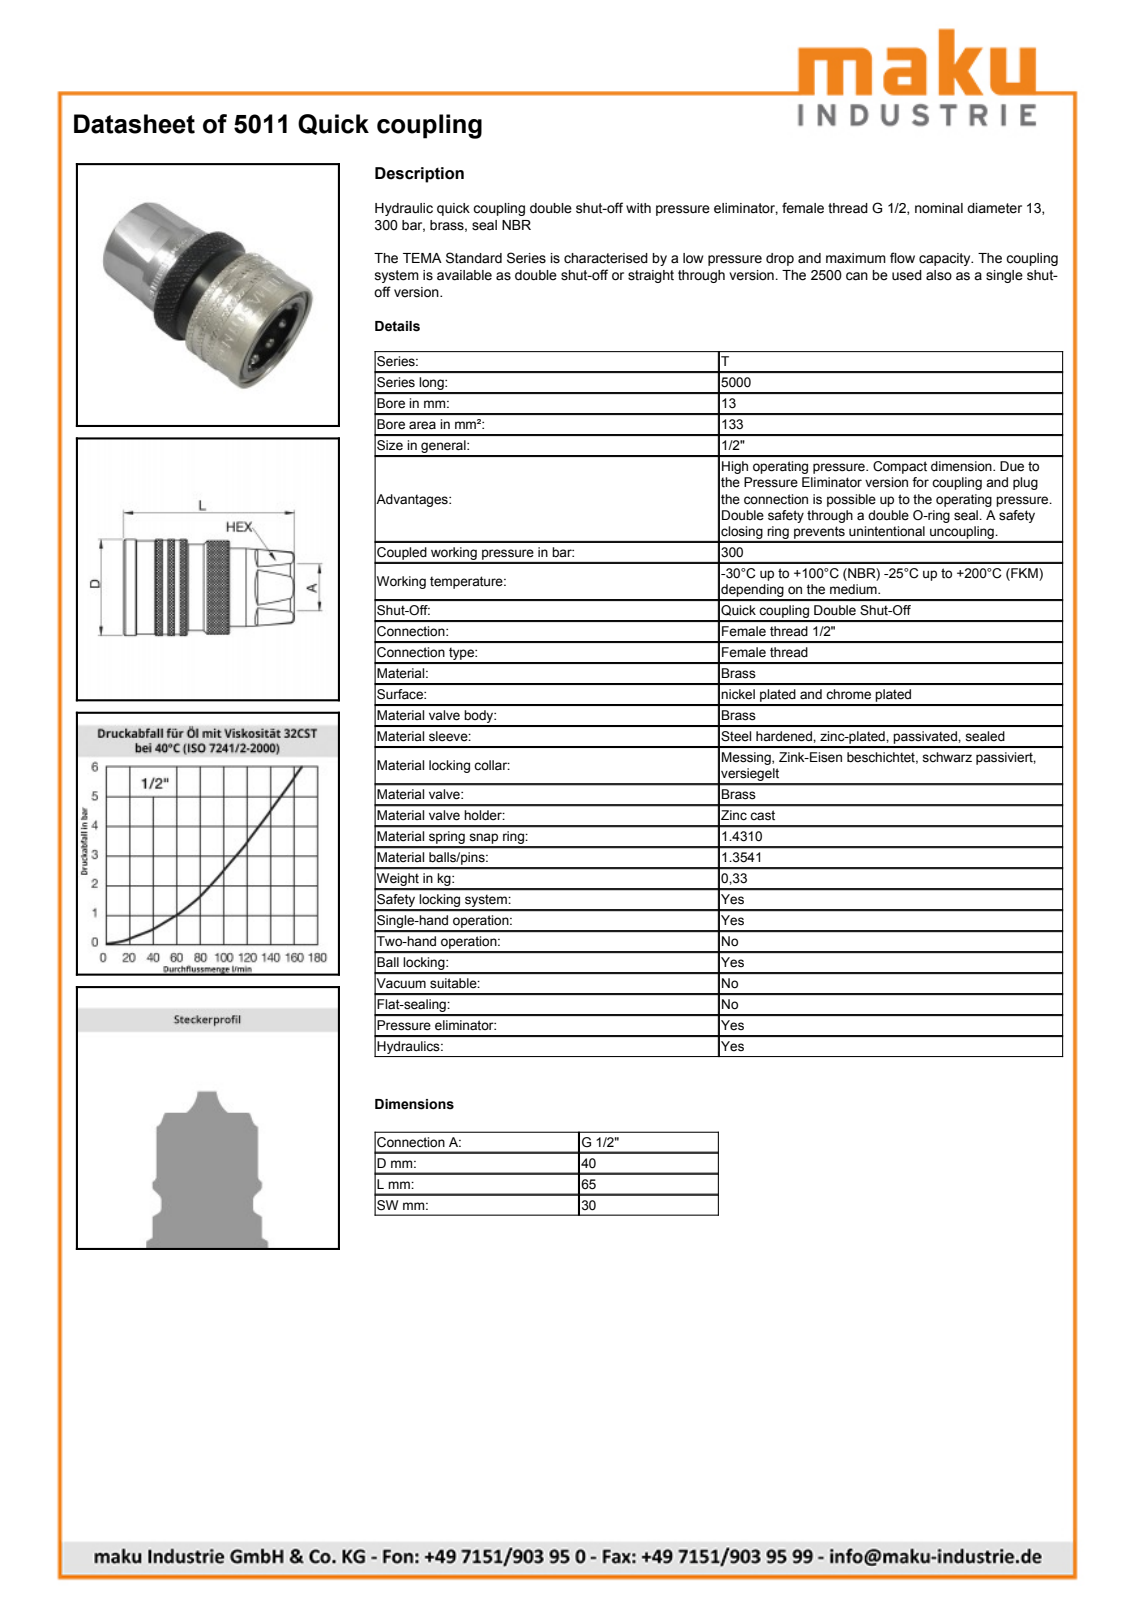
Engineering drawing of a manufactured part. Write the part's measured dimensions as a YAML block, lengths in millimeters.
part_name: "5011"
step_written_by: "SolidWorks 2009 (AUTOMOTIVE_DESIGN)"
units: millimeters
bodies: {solids: 1, faces: 147, planar: 37, cylindrical: 48, other: 62}
overall_size: [65.15, 40, 40]
volume: 47686
surface_area: 14880
round_holes:
  - {diameter: 3.93, count: 1}
  - {diameter: 13.2, count: 1}
  - {diameter: 18.64, count: 1}
  - {diameter: 24.71, count: 1}
  - {diameter: 24.8, count: 1}
  - {diameter: 25.6, count: 1}
  - {diameter: 26.8, count: 1}
  - {diameter: 27.6, count: 1}
  - {diameter: 30.1, count: 1}
  - {diameter: 34.97, count: 1}
  - {diameter: 36.6, count: 1}
round_bosses_or_shafts:
  - {diameter: 40, count: 1}
  - {diameter: 39.2, count: 1}
  - {diameter: 39, count: 1}
  - {diameter: 36.2, count: 1}
  - {diameter: 35.9, count: 1}
  - {diameter: 32.8, count: 1}
face_to_face_distances: [30, 17.25, 11.35, 40, 22.75, 28, 3.2, 13.65, 8.15, 51.35]
